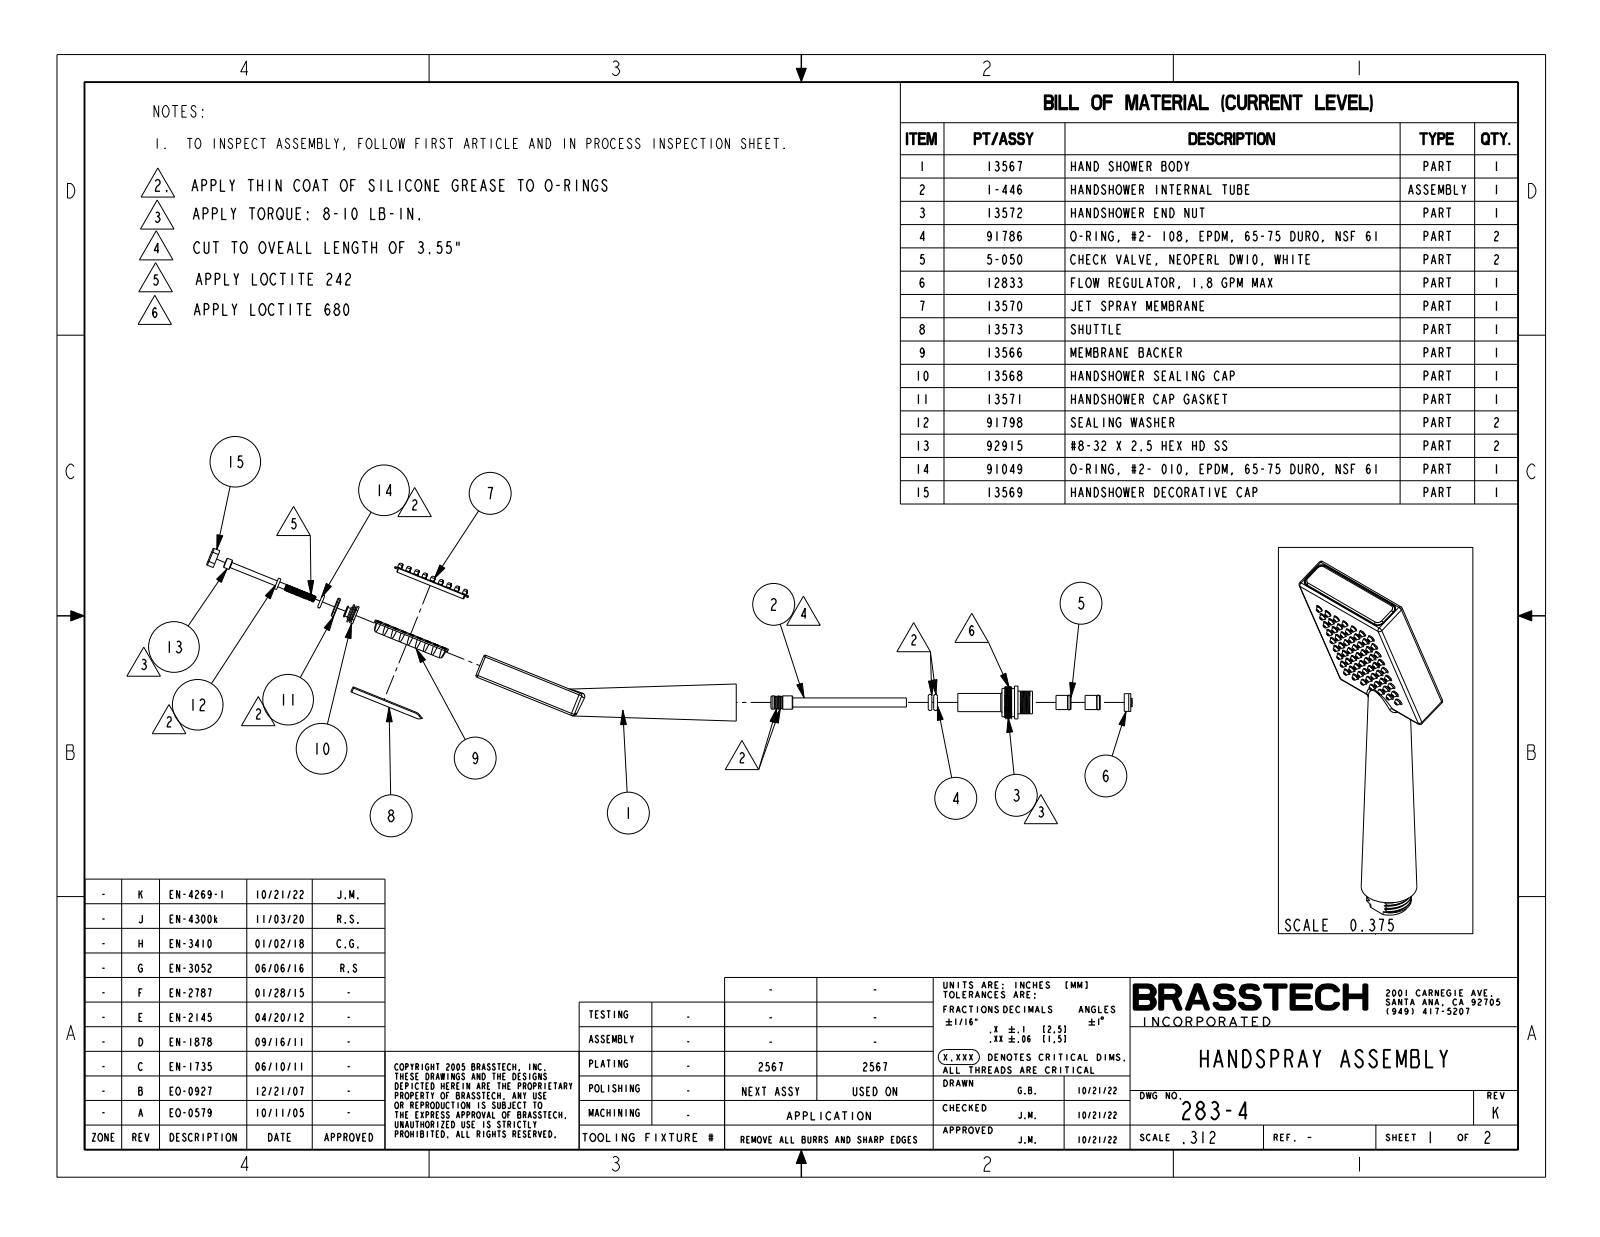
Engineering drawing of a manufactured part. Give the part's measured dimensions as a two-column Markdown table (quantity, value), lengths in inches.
| quantity | value |
| --- | --- |
| part name | 283-4 |
| STEP written by | CREO PARAMETRIC BY PTC INC, 2019352 (CONFIG_CONTROL_DESIGN) |
| units | inches |
| bodies | 1 solid, 604 faces (142 planar, 282 cylindrical, 180 other) |
| overall size | 7.549 × 2.125 × 1.81 |
| volume | 6.918 in³ |
| surface area | 33.4 in² |
| round holes (diameter × count) | 0.03 × 63 |
| round bosses / shafts (diameter × count) | 0.11 × 63 |
| partial cylindrical surfaces (radius × count) | 0.05 × 10, 0.03 × 4, 0.08 × 2, 0.35 × 1, 0.409 × 1 |
| main face-to-face distances | 0.651, 2.125, 2.93, 0.39, 0.625, 2.91, 0.02, 0.061, 0.712, 0.061 |
| hole center spacings | 0.326, 0.528, 0.651, 0.24, 0.48, 0.22, 0.501, 0.753 |
